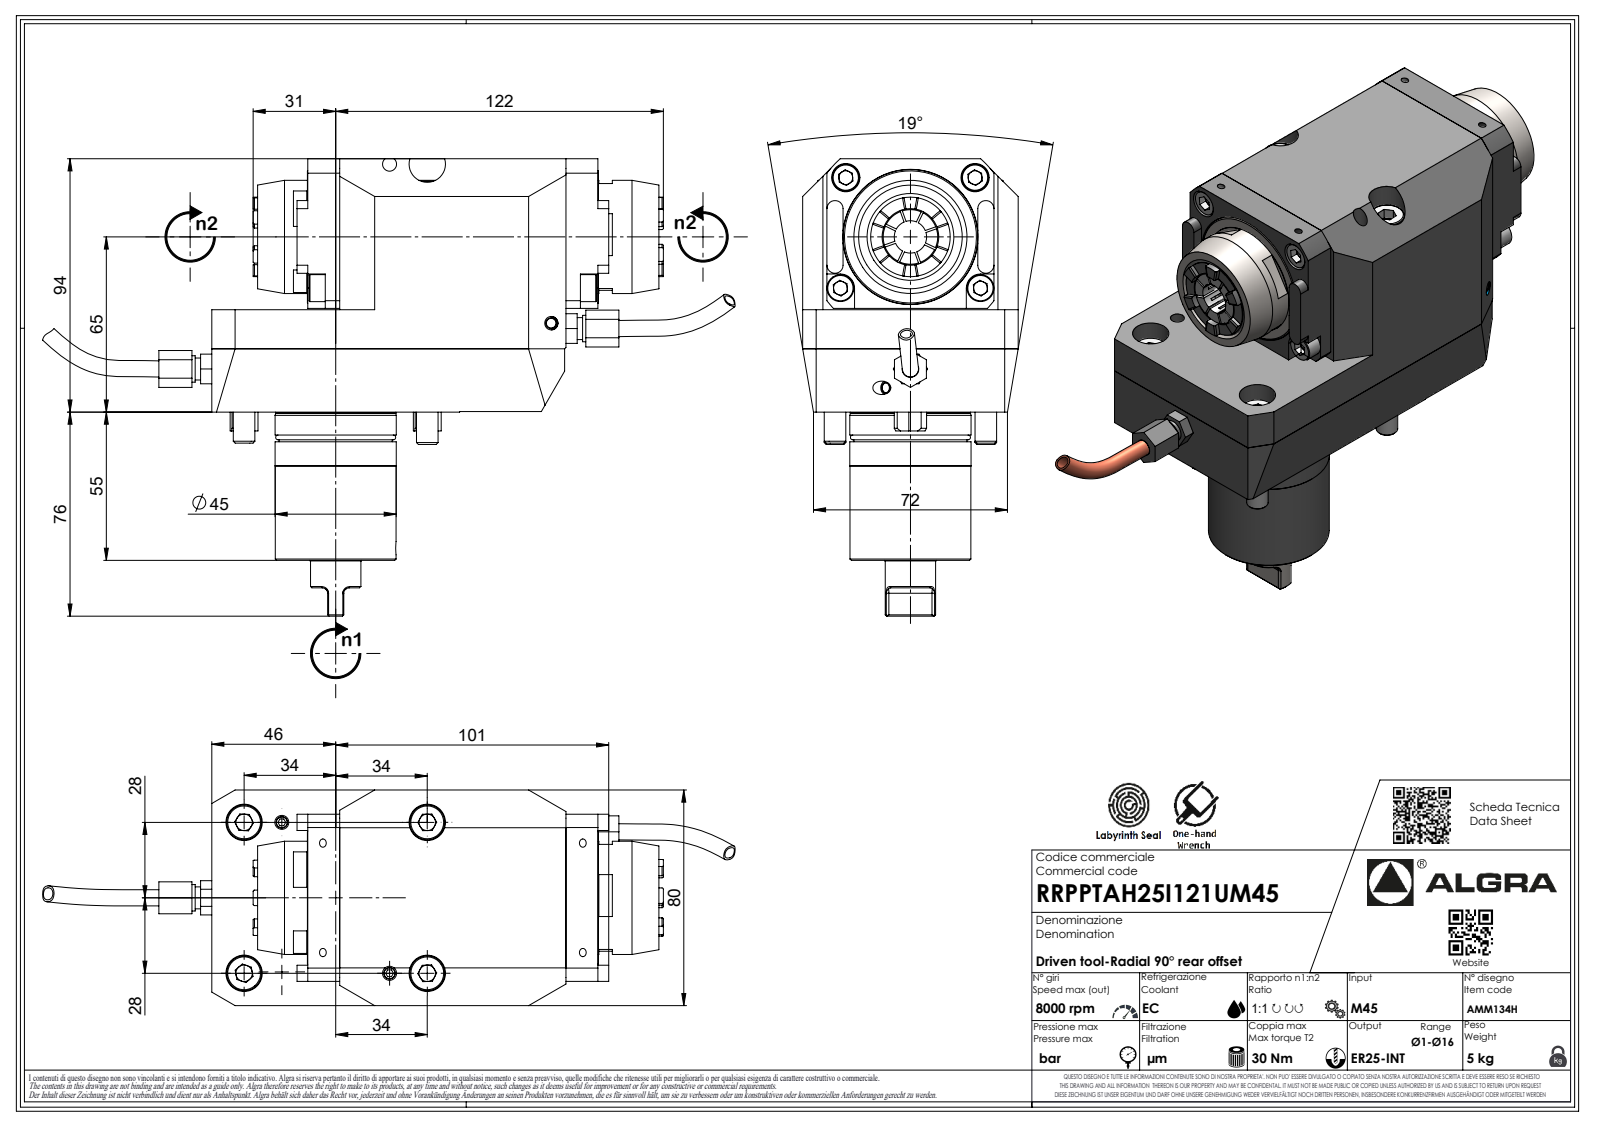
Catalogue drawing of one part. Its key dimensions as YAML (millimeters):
part_name: "RRPPTAH25I121UM45"
step_written_by: "SolidWorks 2023 (AUTOMOTIVE_DESIGN)"
units: millimeters
bodies: {solids: 1, faces: 517, planar: 370, cylindrical: 64, other: 83}
overall_size: [169.7, 166, 80]
volume: 957757
surface_area: 71554
round_holes:
  - {diameter: 2.1, count: 1}
round_bosses_or_shafts:
  - {diameter: 42, count: 2}
  - {diameter: 45, count: 1}
  - {diameter: 44.85, count: 1}
  - {diameter: 44.6, count: 1}
  - {diameter: 18.7, count: 1}
  - {diameter: 6.37, count: 1}
  - {diameter: 1.7, count: 1}
partial_cylinders:
  - {radius: 0.33, count: 7}
  - {radius: 0.52, count: 7}
  - {radius: 3.7, count: 7}
  - {radius: 2, count: 6}
  - {radius: 3, count: 4}
  - {radius: 6, count: 2}
  - {radius: 0.21, count: 1}
  - {radius: 25.1, count: 1}
face_to_face_distances: [94, 56, 80, 38, 9, 71, 149, 37.8, 93.8, 0.5]
